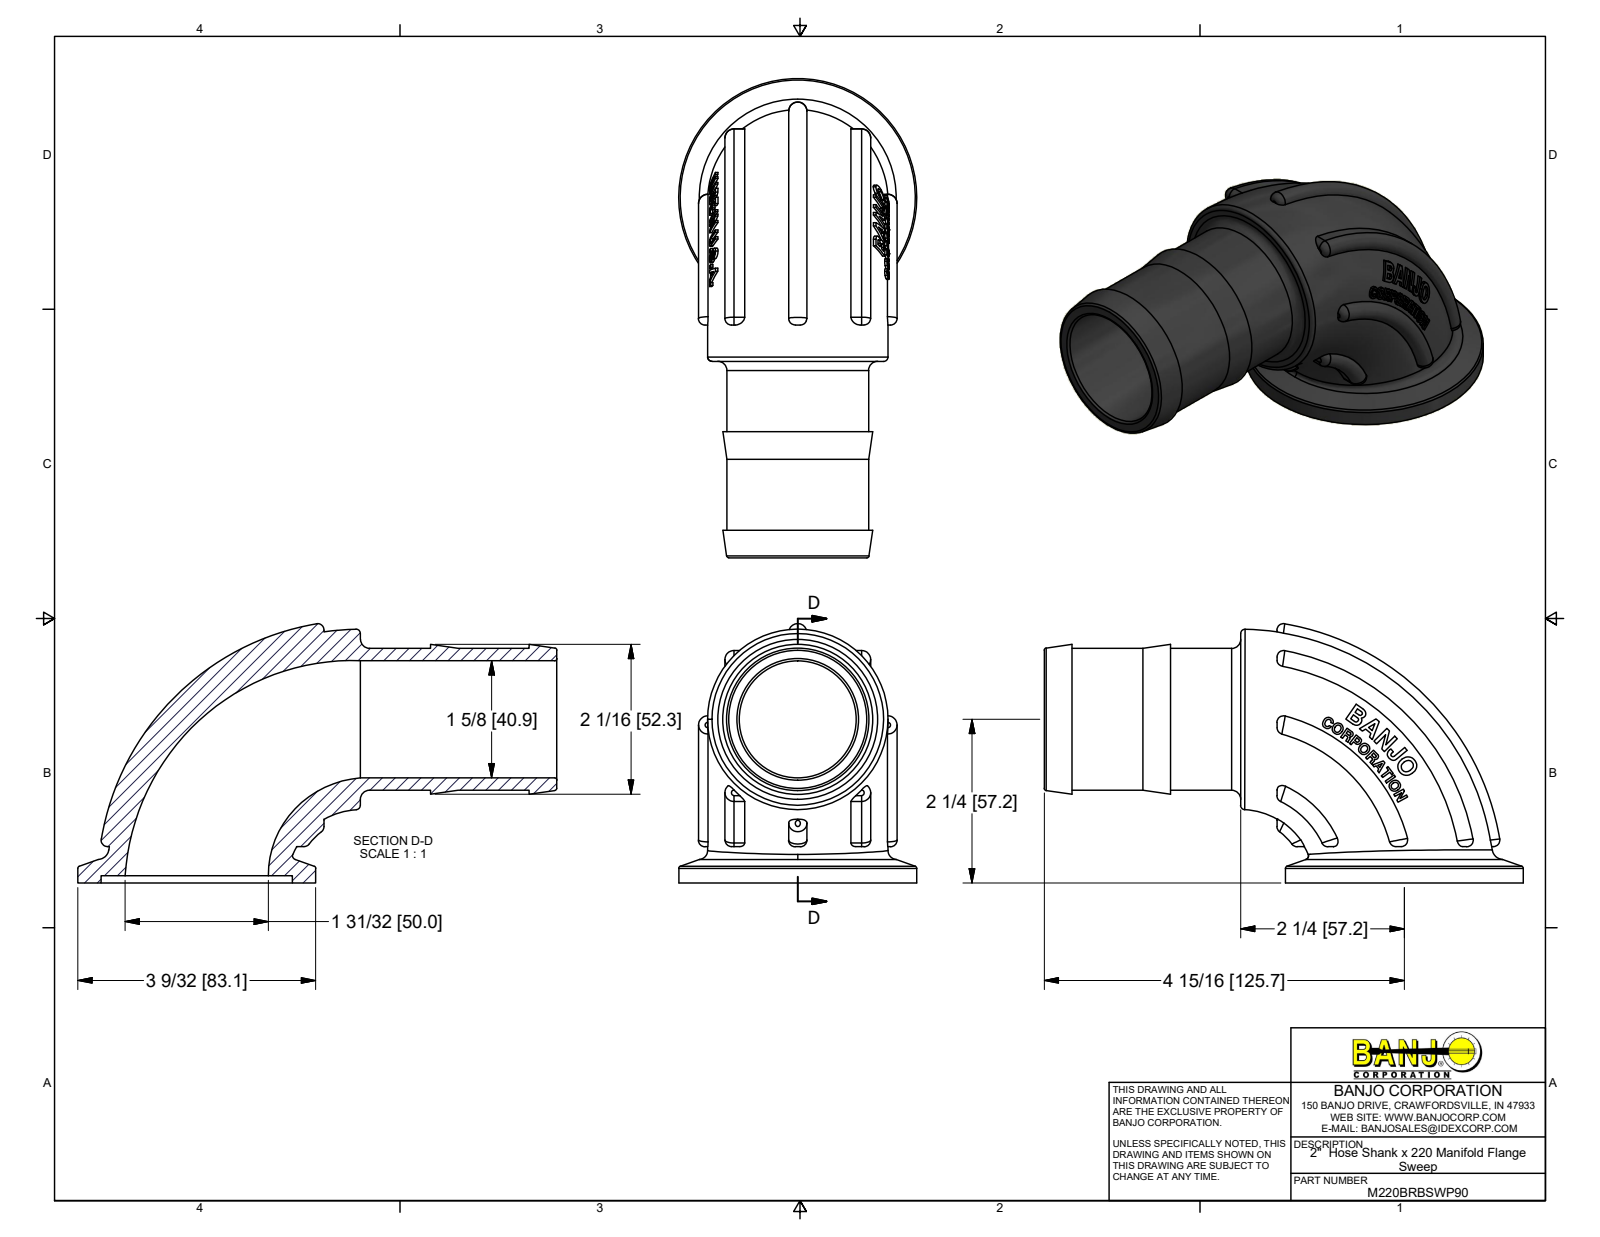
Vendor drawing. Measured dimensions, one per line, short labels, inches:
name: M220BRBSWP90
written by: Autodesk Inventor 2019 (AUTOMOTIVE_DESIGN)
unit: in
bodies: 1 solid, 427 faces (214 planar, 17 cylindrical, 196 other)
size: 6.585 × 3.565 × 3.27
volume: 12.13 in³; area: 93.08 in²
holes: 1× ⌀1.61, 1× ⌀2.63
bosses: 1× ⌀3.27, 1× ⌀1.95
rounds: 4× R0.09, 1× R1.248, 1× R3.252
face distances: 0.1, 2.7, 0.38, 1.735, 1.355, 2.32, 0.965, 0.5, 0.041, 3.2
